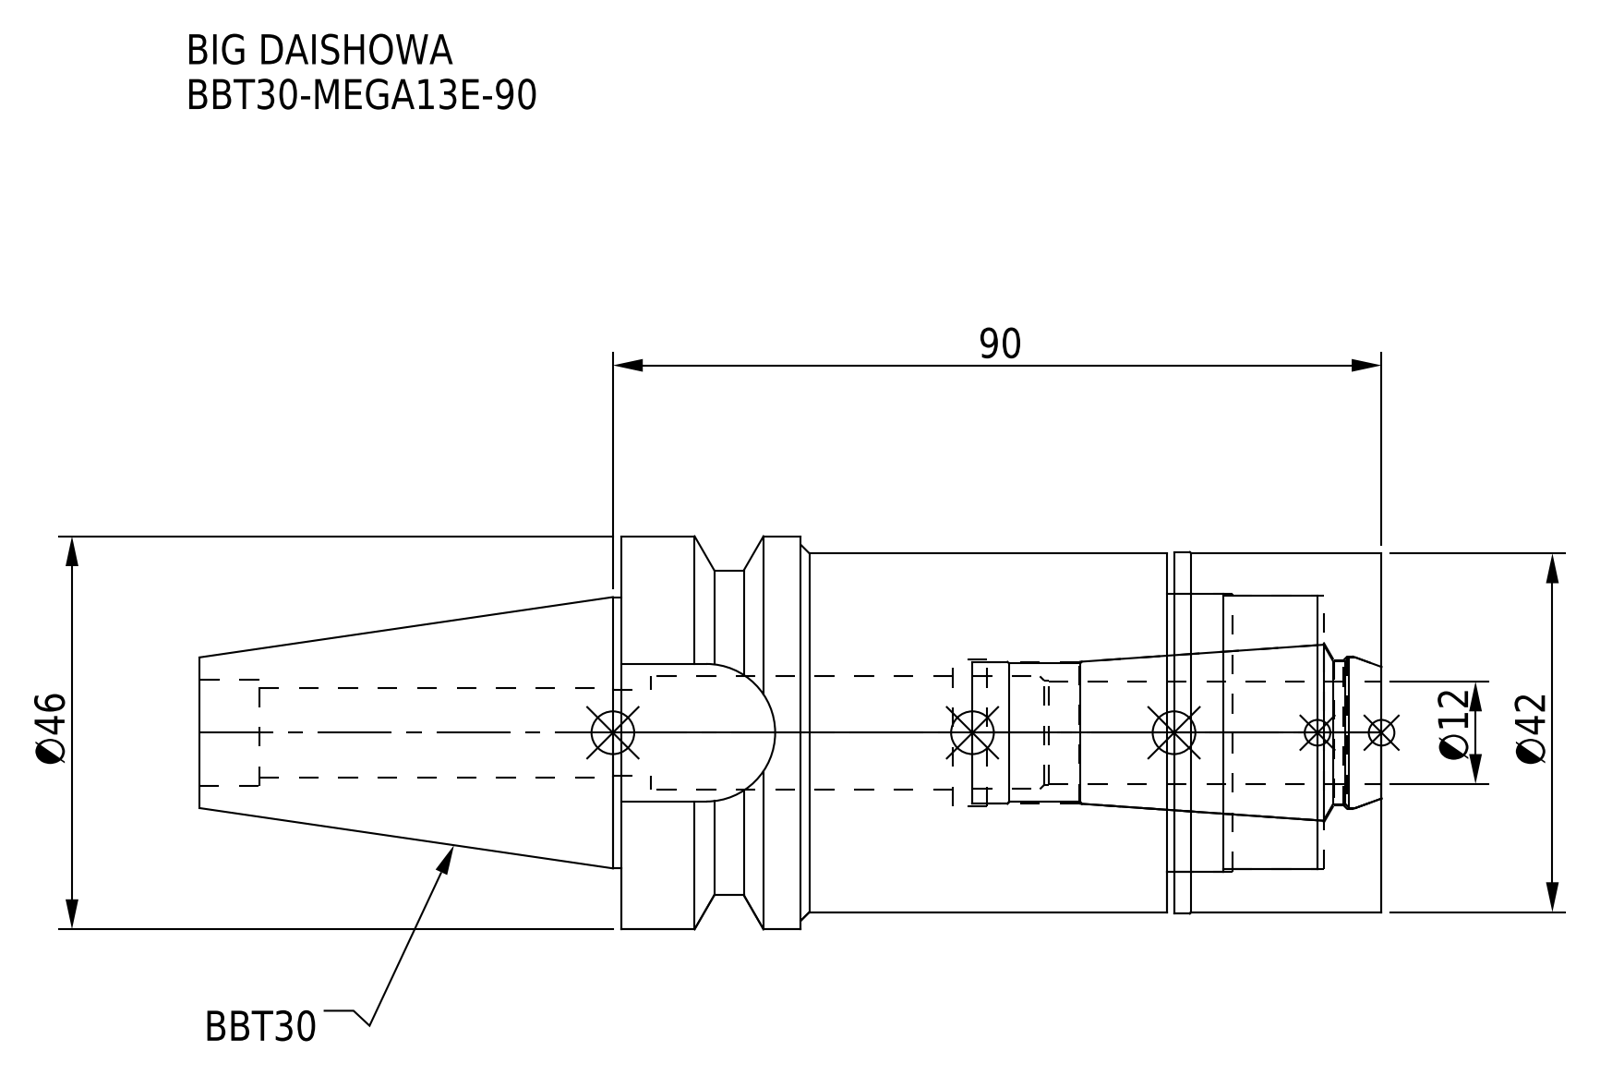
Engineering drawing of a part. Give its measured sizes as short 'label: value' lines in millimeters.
name: MEN13_1.stp; BBT30-MEGA13E-90_1.stp; DXF_TEMP_ASSY_ASM_4_ASM.stp; BBT30ME13090-120_ASM.stp (+3 more)
written by: SolidWorks 2019 (CONFIG_CONTROL_DESIGN)
unit: mm
bodies: 2 solids, 79 faces (21 planar, 40 cylindrical, 18 other)
size: 138.4 × 46 × 46
volume: 125 040 mm³; area: 30 711 mm²
holes: 1× ⌀10, 1× ⌀10.4, 1× ⌀12.5, 1× ⌀13.3, 1× ⌀16.6, 1× ⌀17, 1× ⌀17.2, 1× ⌀17.9, 1× ⌀32, 1× ⌀32.5
bosses: 1× ⌀46, 1× ⌀42.3, 1× ⌀42, 1× ⌀31.75
rounds: 1× R8.05, 1× R19
face distances: 89, 25.1, 24.3, 64.7, 0.8, 63.9, 17.5, 6.8, 7.5, 16.8
